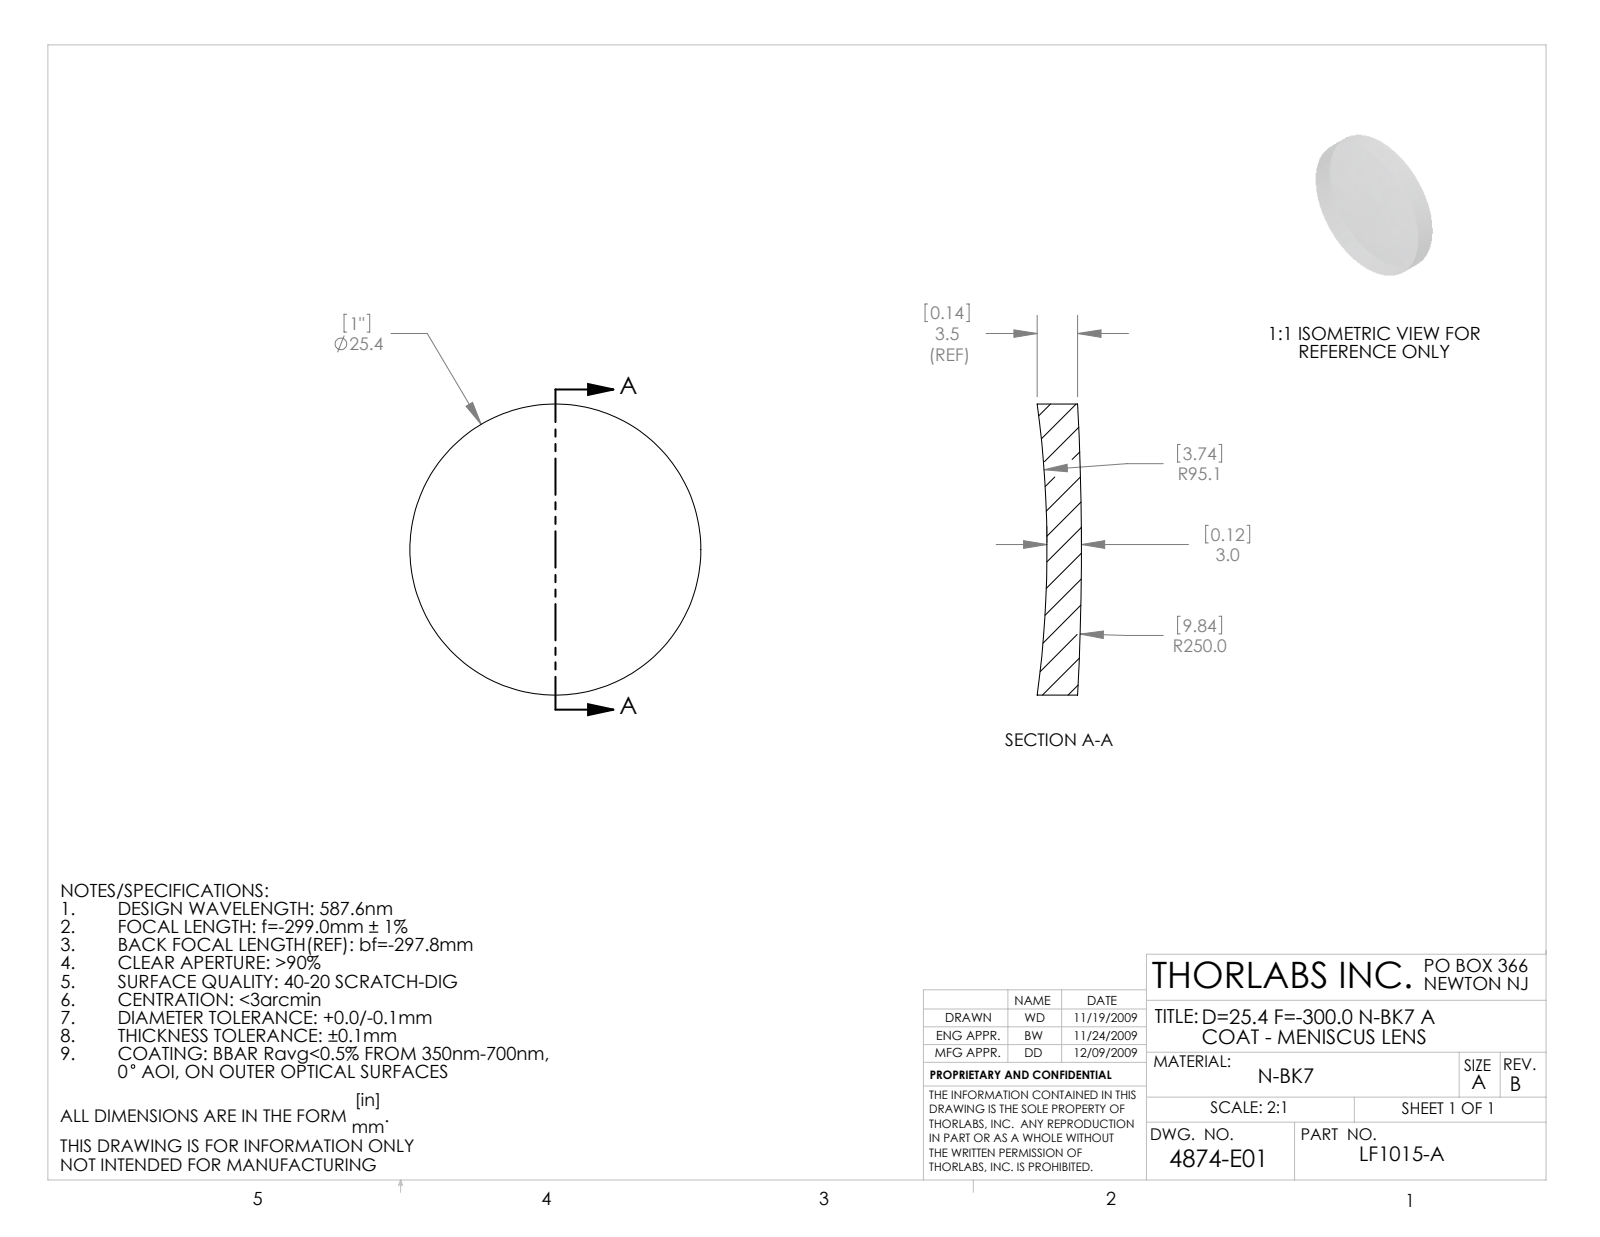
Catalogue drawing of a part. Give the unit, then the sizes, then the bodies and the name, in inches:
Units: inches
Overall size (bounding box): 1 × 1 × 0.152
Round bosses / shafts (diameter × count): ⌀1 ×1
Volume: 0.101 in³ · Surface area: 2.012 in²
Bodies: 1 solid, 6 faces (0 planar, 2 cylindrical, 4 other)
Part name (STEP PRODUCT): 4874-E0W
STEP written by: SolidWorks 2009 (AUTOMOTIVE_DESIGN)
